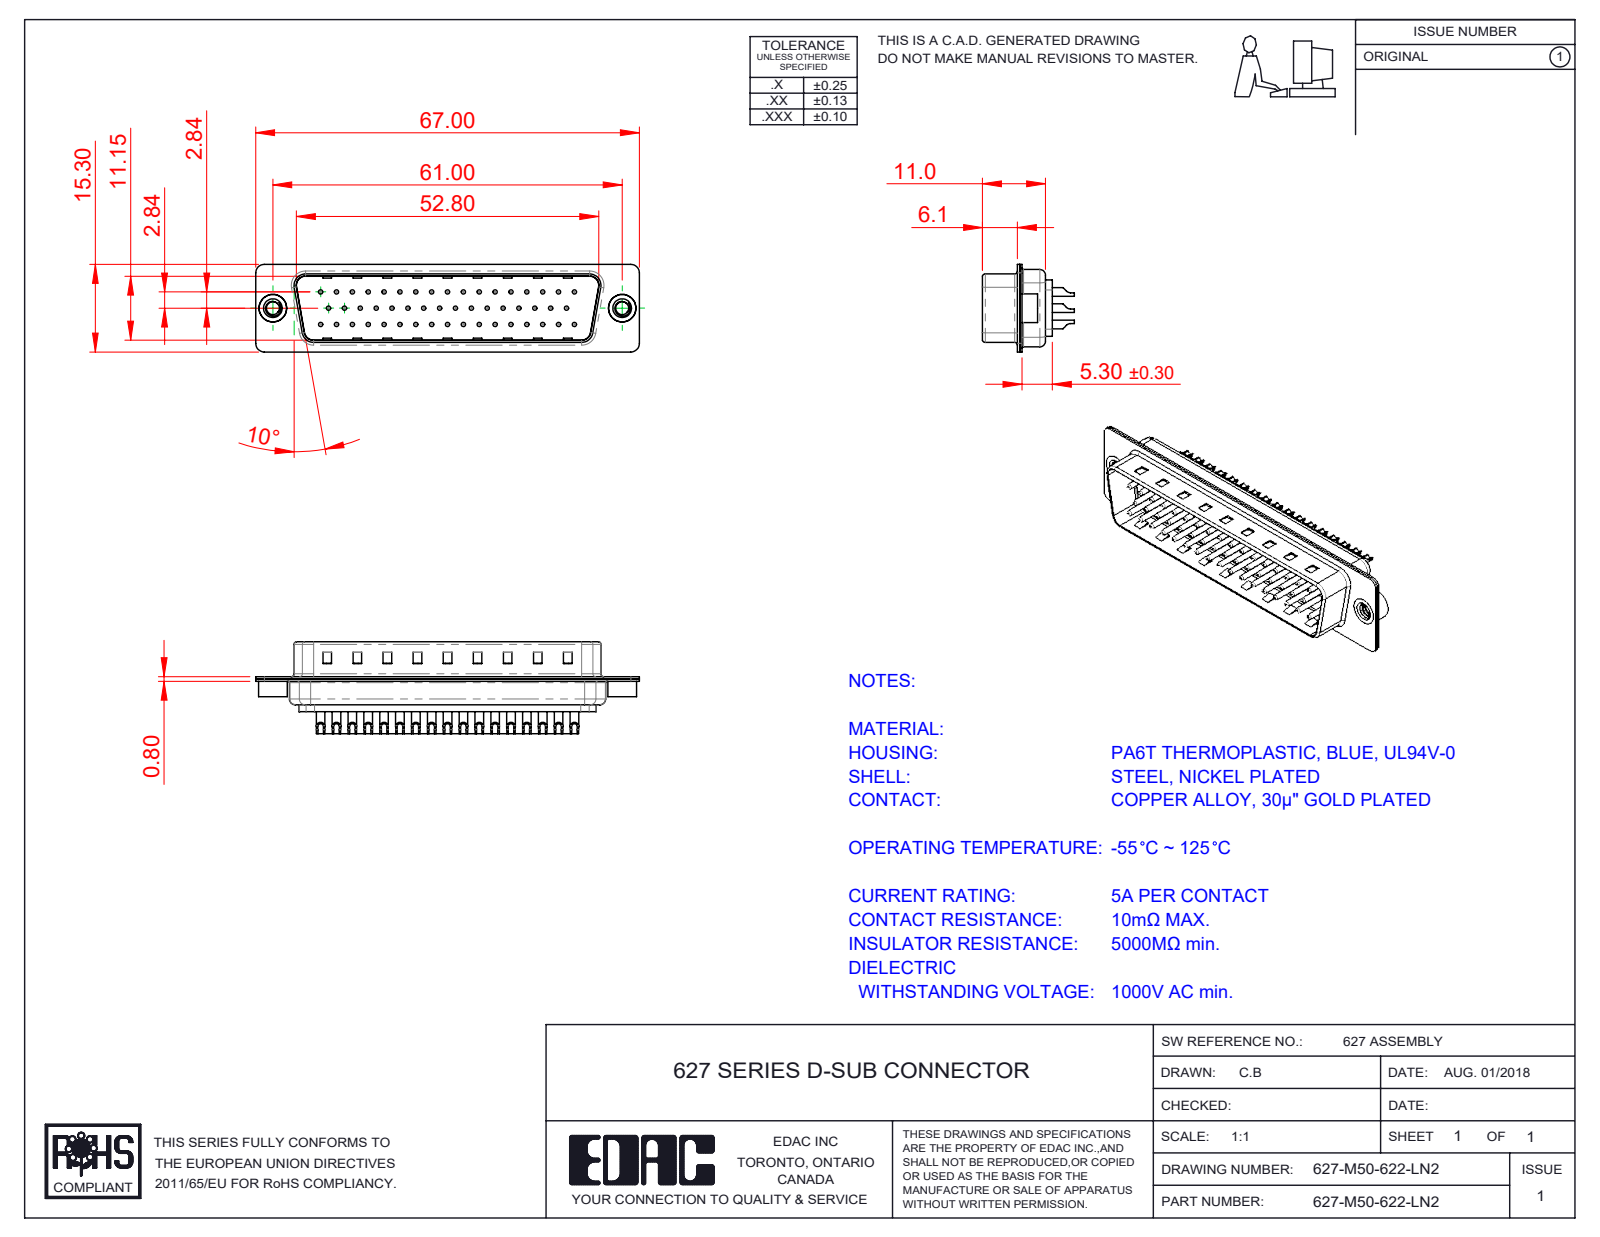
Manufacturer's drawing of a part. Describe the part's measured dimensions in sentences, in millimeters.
The part is named "627M Contact Row 3_22; 627-M50-622-LN2; 627M Shell Rear_50 Contacts; 627M Housing_50 Contacts (+4 more)". Its 3-D file was written by "SolidWorks 2020 (CONFIG_CONTROL_DESIGN)". It is 55 solids with 2262 faces: 653 planar, 941 cylindrical and 668 other. Overall it measures 67 by 16.05 by 15.3 millimeters. Its volume is 4 639 cubic millimeters and its surface area 11 168 square millimeters. Round holes: 50 of diameter 0.75, 50 of diameter 1, 50 of diameter 1.6, 50 of diameter 2, 2 of diameter 2.26, 2 of diameter 4, 2 of diameter 4.8. Round bosses or shafts: 50 of diameter 1.5, 2 of diameter 5, 2 of diameter 4.9. Partial cylindrical surfaces (rounded edges, fillets, slot ends): 16 of radius 1.5, 12 of radius 2, 8 of radius 0.5, 8 of radius 1.6, 7 of radius 1, 4 of radius 0.25, 4 of radius 0.6, 4 of radius 0.65. The main face-to-face distances are 0.4, 11.55, 5.7, 6.1, 0.78, 0.77, 12.33, 12.32, 13.1, 5.3. The hole center spacings are 3.16, 2.77, 5.54, 8.31, 11.08, 13.85, 16.62, 5.03.
